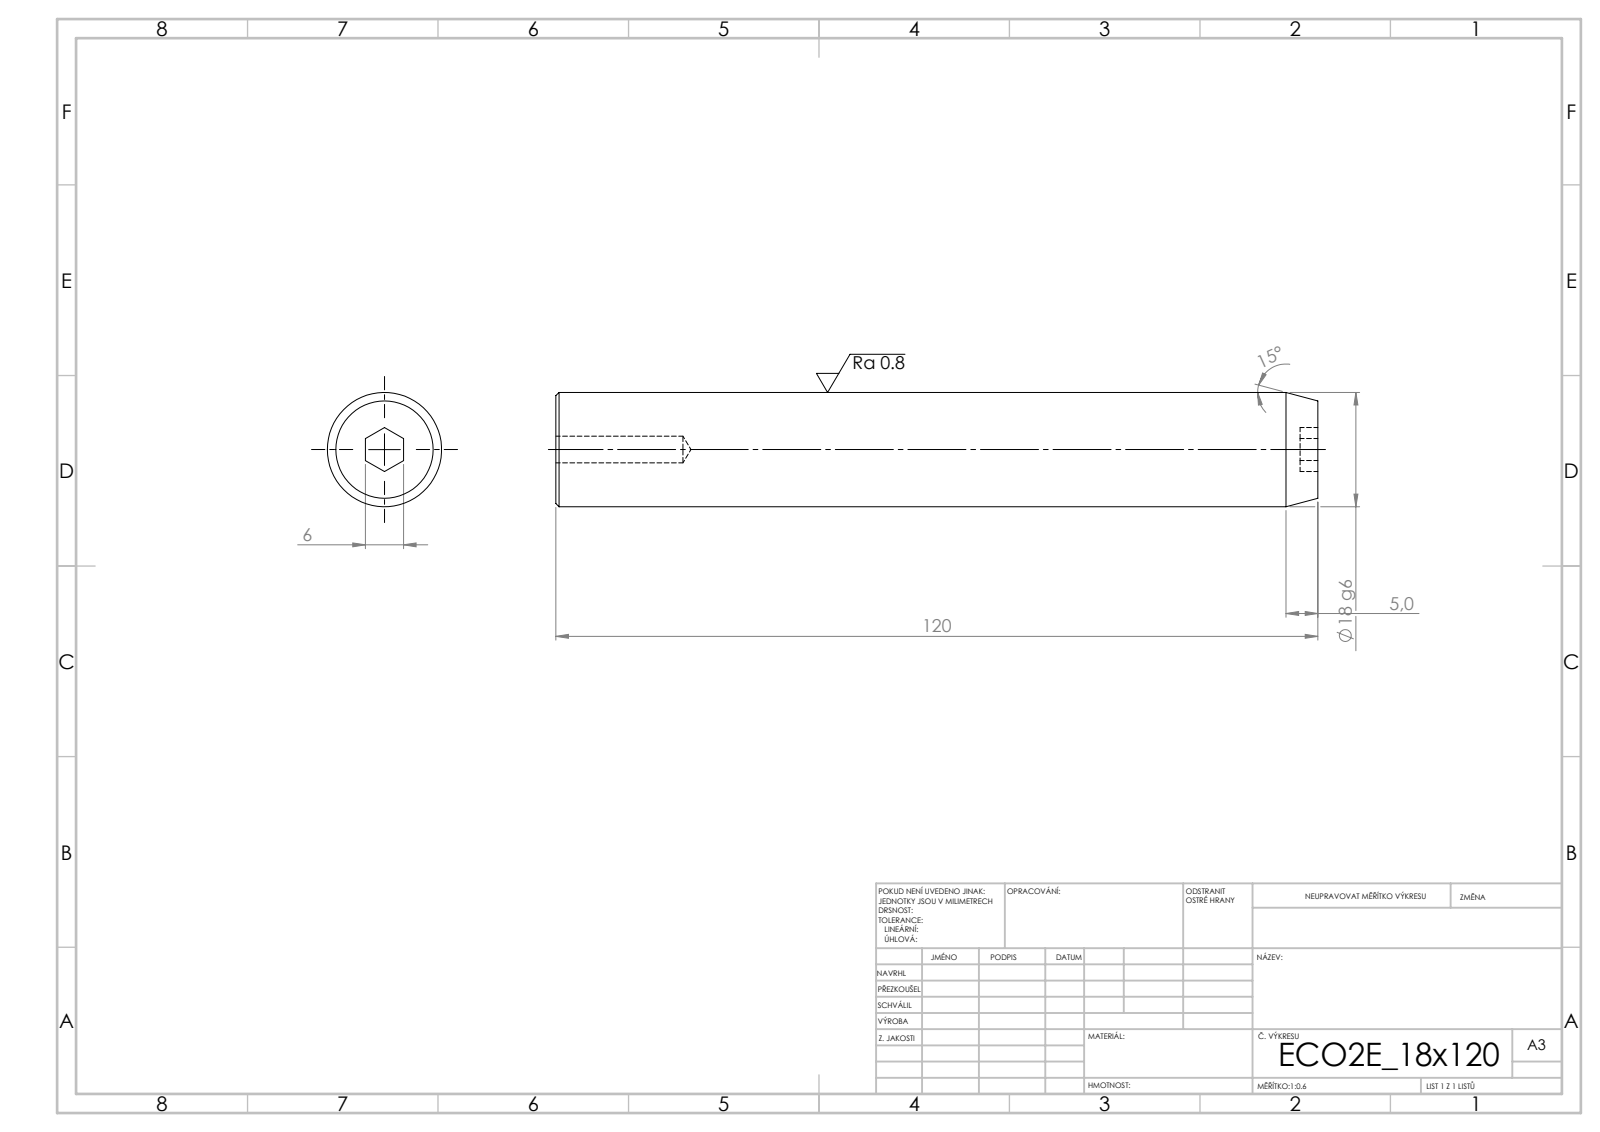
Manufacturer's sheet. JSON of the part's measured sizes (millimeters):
{"step_written_by": "SolidWorks 2019 (CONFIG_CONTROL_DESIGN)", "units": "millimeters", "bodies": {"solids": 1, "faces": 19, "planar": 9, "cylindrical": 4, "other": 6}, "overall_size": [120, 18, 18], "volume_mm3": 29979, "surface_area_mm2": 7520, "round_holes": [[4.2, 1]], "round_bosses_or_shafts": [[18, 1]], "face_to_face_distances": [120, 2.8, 117.2, 6]}
